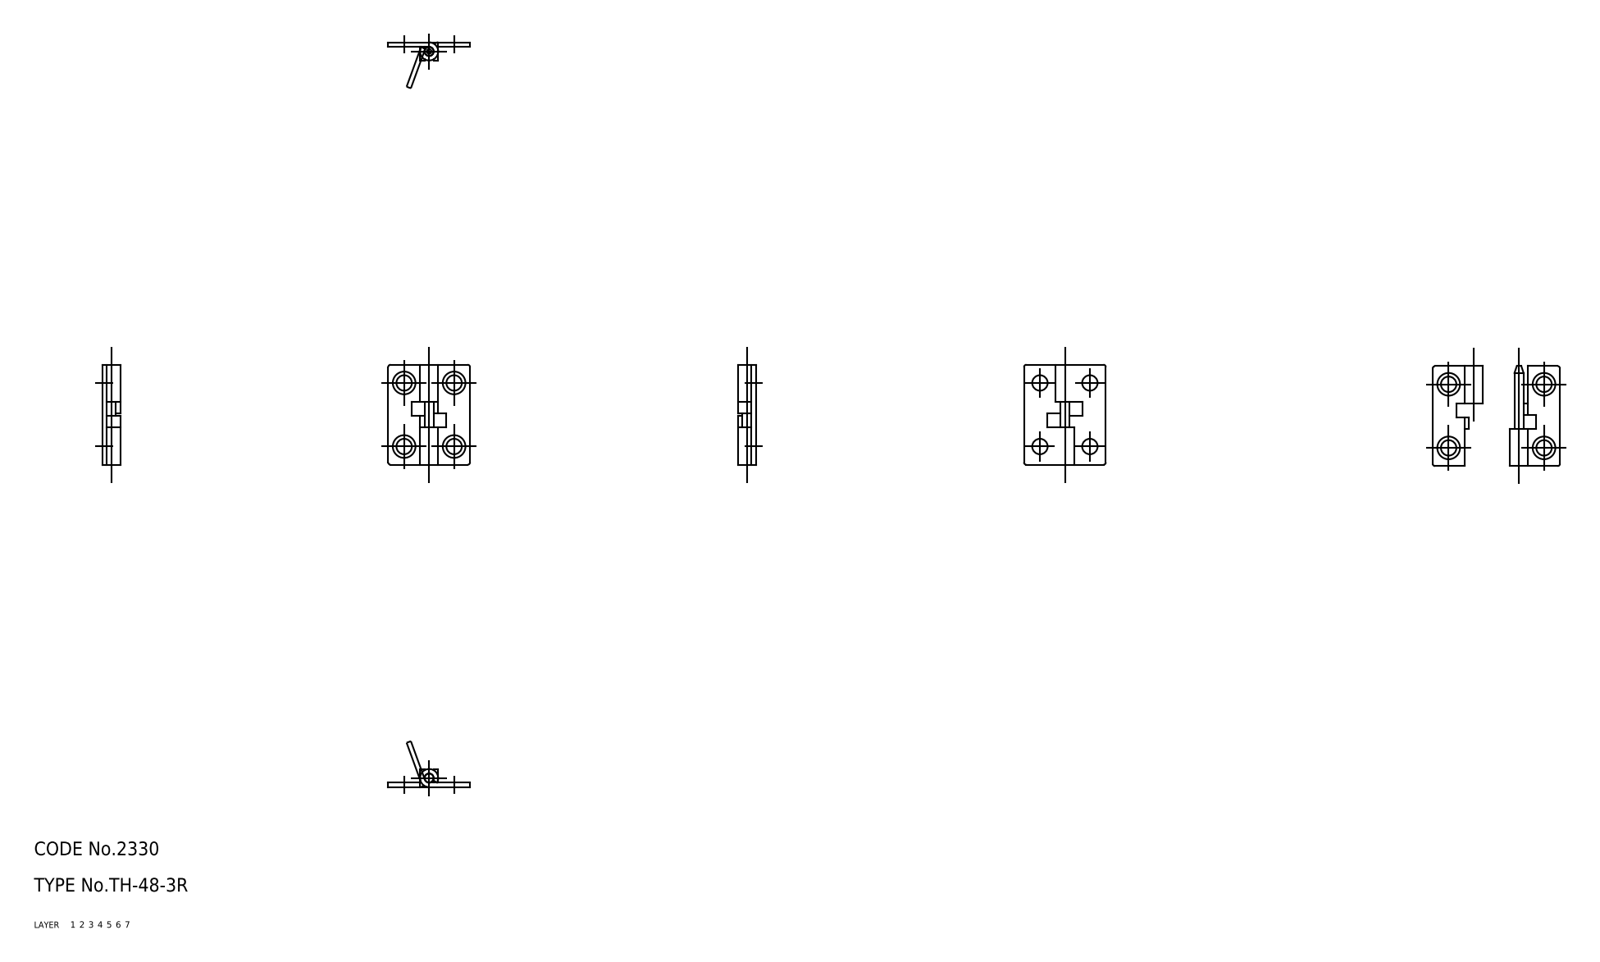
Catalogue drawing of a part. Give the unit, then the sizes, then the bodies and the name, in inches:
Units: inches
Overall size (bounding box): 0.866 × 0.709 × 0.157
Volume: 0.03 in³ · Surface area: 1.897 in²
Bodies: 3 solids, 60 faces (0 planar, 0 cylindrical, 60 other)
Part name (STEP PRODUCT): 67112038; 67112051; 67112064
STEP written by: CADfix (AUTOMOTIVE_DESIGN)
